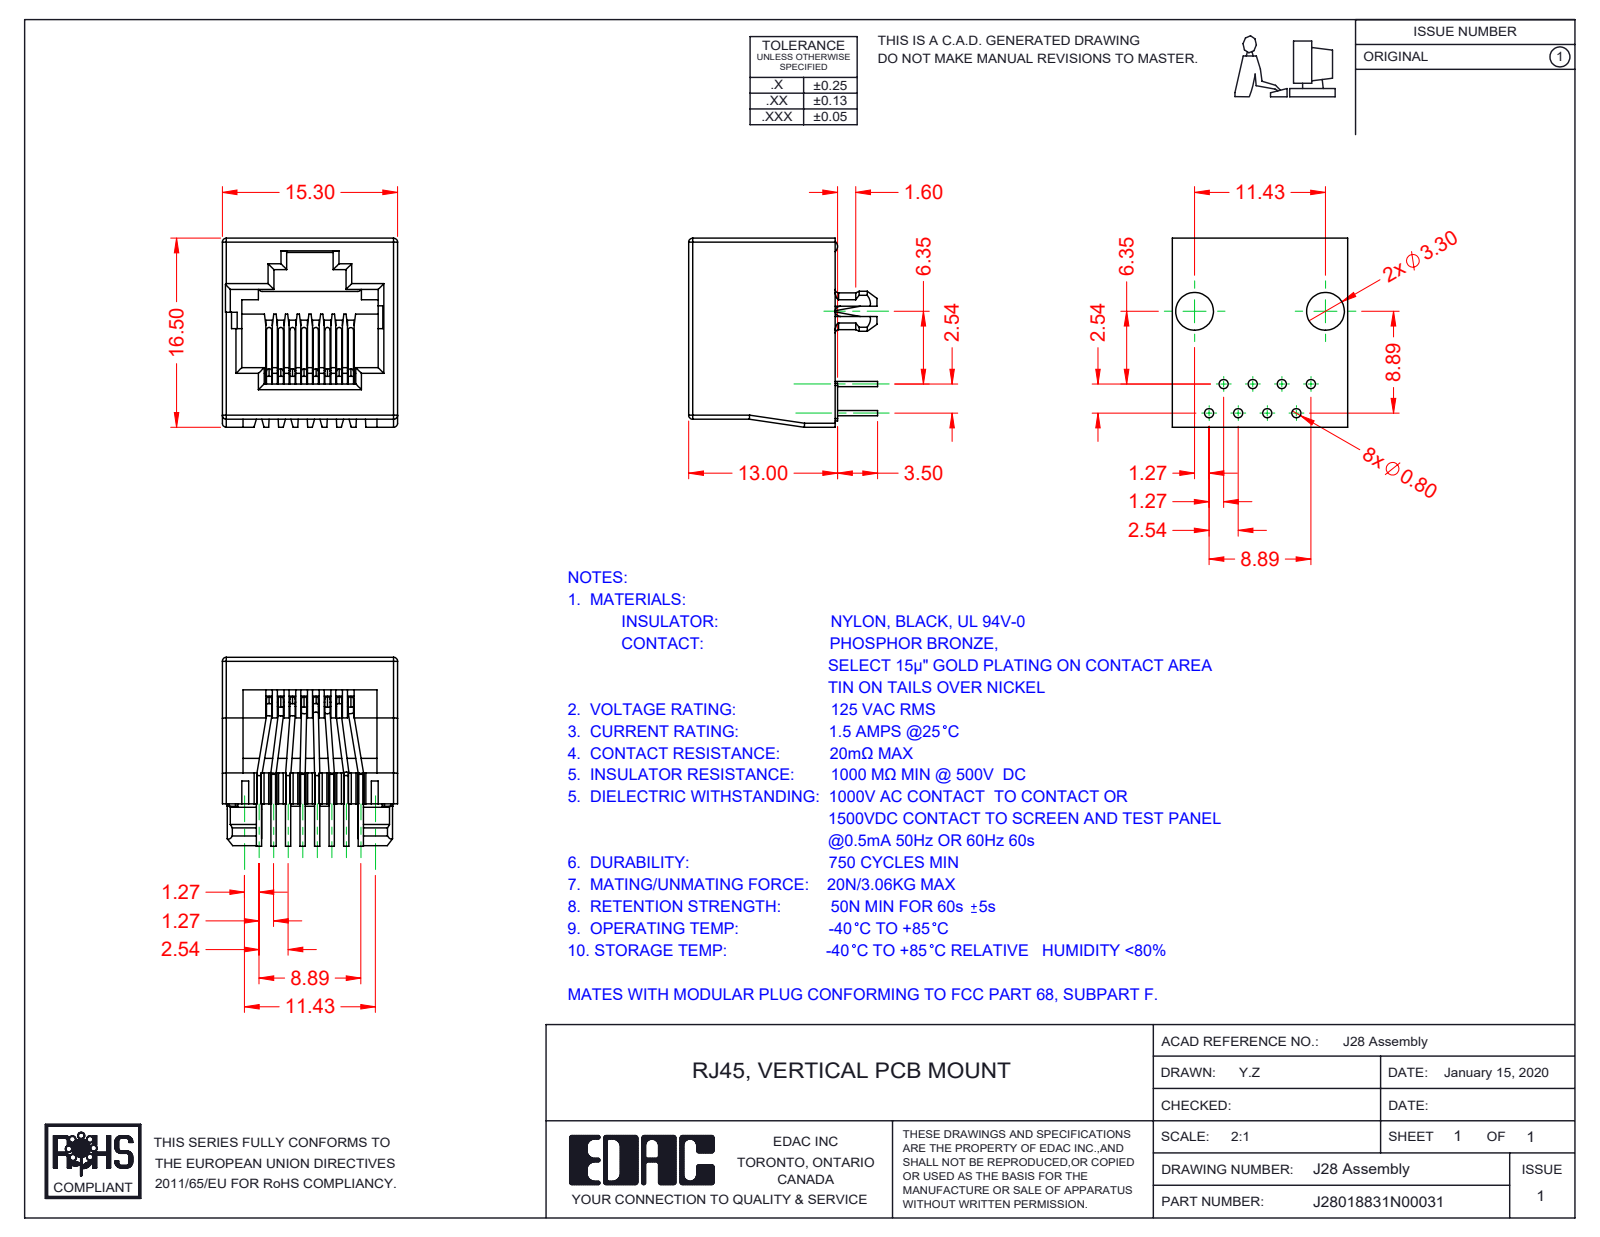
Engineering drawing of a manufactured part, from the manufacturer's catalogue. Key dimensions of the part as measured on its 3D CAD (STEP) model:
Part name (STEP PRODUCT): 28 Insulator; 28 Contacts; RJ28018831N00031
STEP written by: SolidWorks 2016 (CONFIG_CONTROL_DESIGN)
Units: millimetres
Bodies: 9 solids, 580 faces (319 planar, 205 cylindrical, 56 other)
Overall size (bounding box): 16.5 × 16.5 × 15.3
Volume: 1 535 mm³ · Surface area: 2 745 mm²
Round holes (diameter × count): ⌀1.6 ×2
Round bosses / shafts (diameter × count): ⌀0.46 ×45
Partial cylindrical surfaces — rounded edges, fillets, slot ends (radius × count): R0.5 ×19, R0.1 ×16, R0.35 ×14, R0.25 ×10, R0.2 ×8, R0.23 ×8, R0.45 ×2, R1.6 ×2
Main face-to-face distances: 15.3, 1.02, 1.7, 13.6, 1.25, 2.04, 12.81, 3.06, 3.15, 12.15
Hole centre spacings: 12
